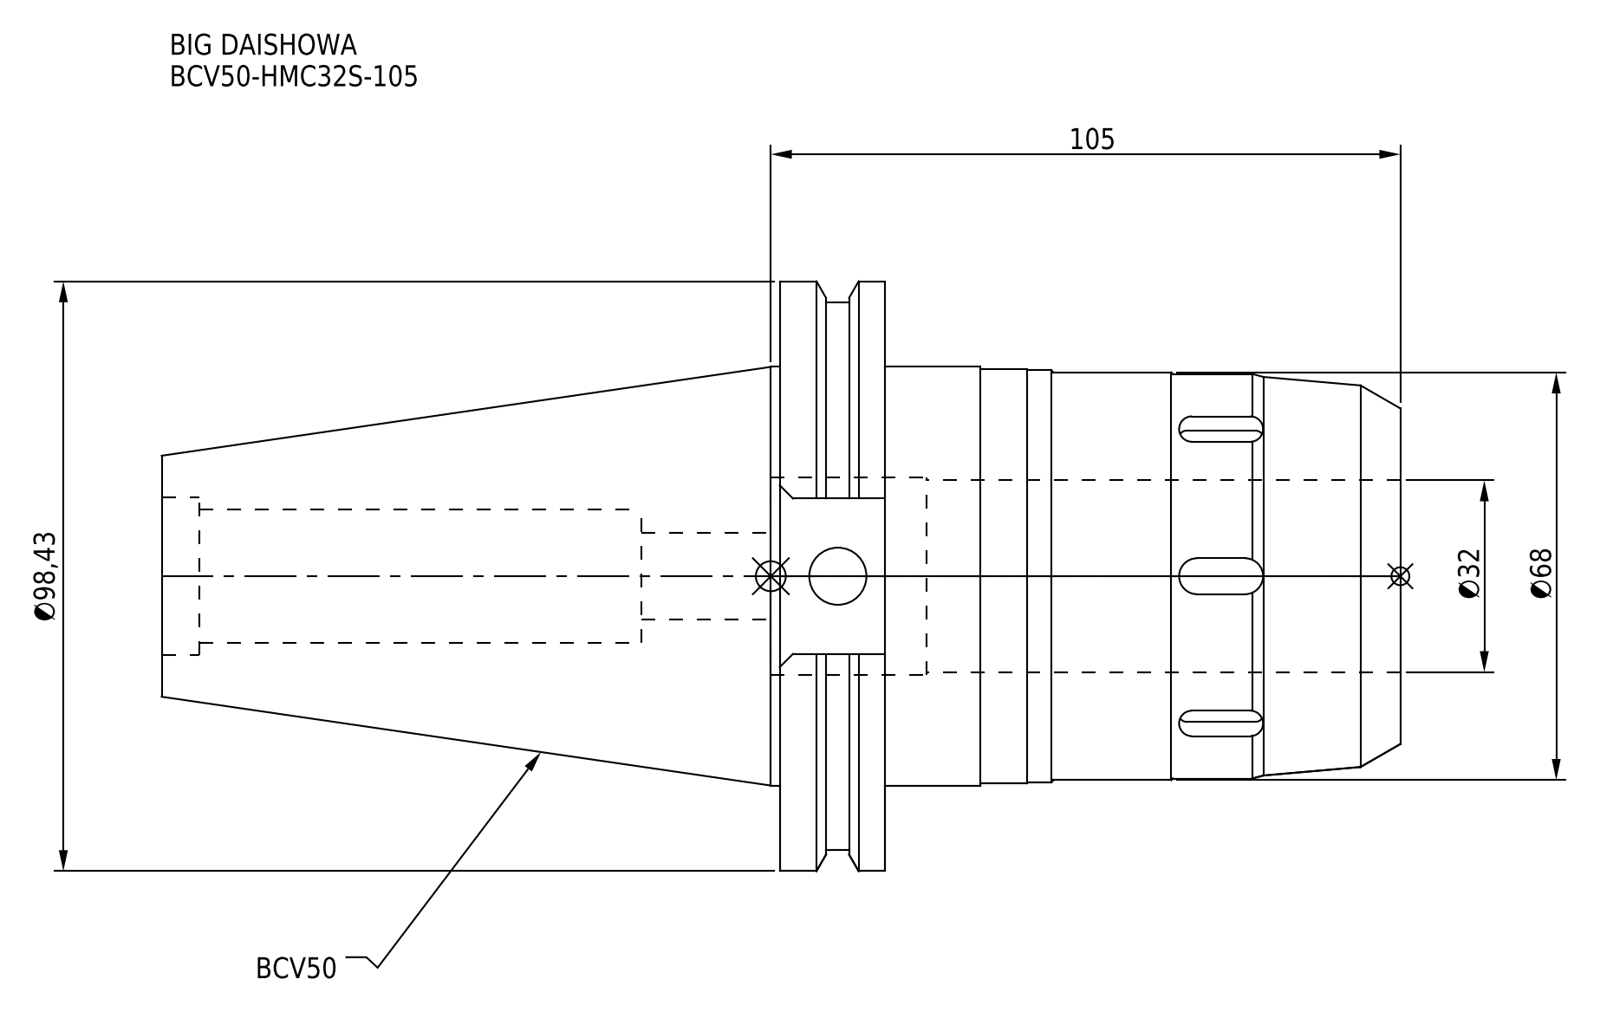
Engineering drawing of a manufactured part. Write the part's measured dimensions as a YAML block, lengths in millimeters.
part_name: "BCV50-HMC32S-105"
step_written_by: "CREO PARAMETRIC BY PTC INC, 2016380 (AUTOMOTIVE_DESIGN)"
units: millimeters
bodies: {solids: 1, faces: 111, planar: 49, cylindrical: 46, other: 16}
overall_size: [206.6, 98.43, 94.96]
volume: 553489
surface_area: 71427
round_holes:
  - {diameter: 9.53, count: 1}
  - {diameter: 14.5, count: 1}
  - {diameter: 22.3, count: 1}
  - {diameter: 26.23, count: 1}
  - {diameter: 32, count: 1}
  - {diameter: 33, count: 1}
round_bosses_or_shafts:
  - {diameter: 98.43, count: 1}
  - {diameter: 91.29, count: 1}
  - {diameter: 69.85, count: 1}
  - {diameter: 69, count: 1}
  - {diameter: 68.7, count: 1}
  - {diameter: 68, count: 1}
  - {diameter: 67.5, count: 1}
partial_cylinders:
  - {radius: 3, count: 12}
face_to_face_distances: [17.55, 85.95, 103.5, 206.6, 120.65, 103.1, 105, 19.05, 1.5, 101.6]
